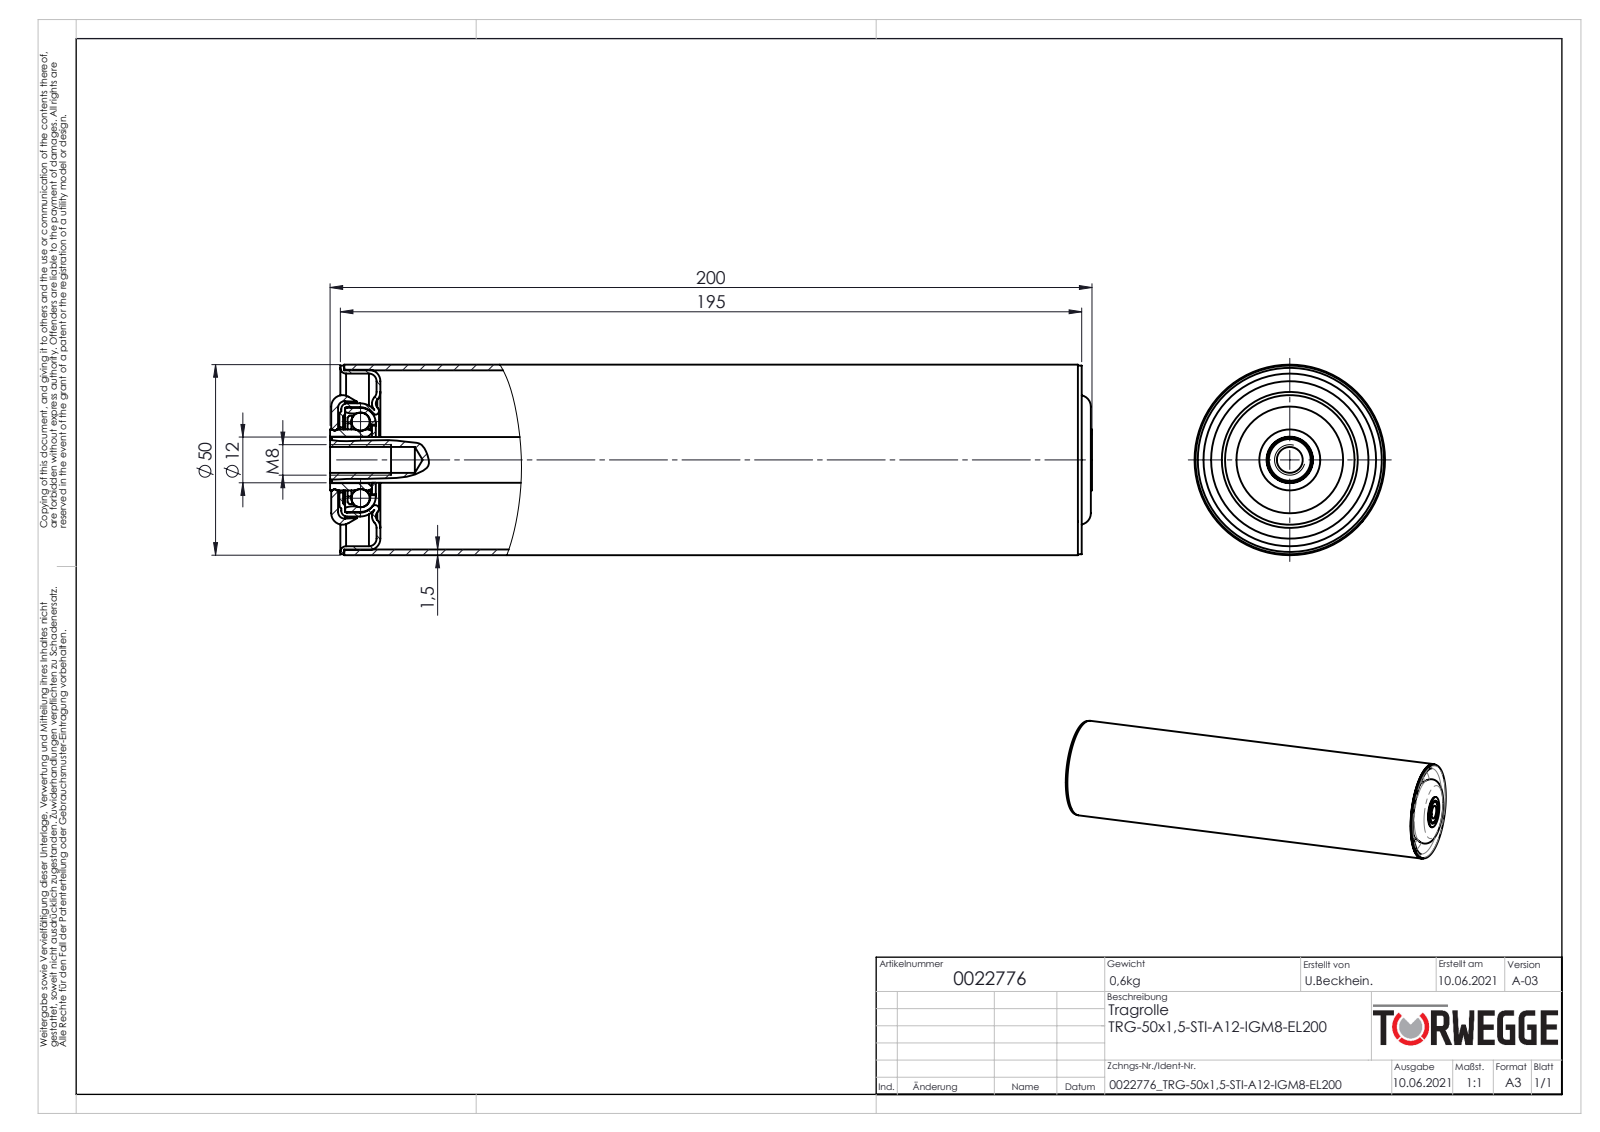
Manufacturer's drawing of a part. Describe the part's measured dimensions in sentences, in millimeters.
The part is named "0022776; 0026293_Typ-TRG-50x1,5-12; 0039771_Tragrollenrohr-Ø50x1,5STI_KFG_EL200; 0039780-Achse-ST-Ø12-KFG_IGM8-AL=200 (+1 more)". Its 3-D file was written by "SolidWorks 2020 (AUTOMOTIVE_DESIGN)". It is 30 solids with 498 faces: 92 planar, 102 cylindrical and 304 other. Overall it measures 200 by 50 by 50 millimeters. Its volume is 81 860 cubic millimeters and its surface area 97 629 square millimeters. Round holes: 1 of diameter 6.8, 1 of diameter 12, 1 of diameter 12.2, 1 of diameter 17.1, 1 of diameter 18.5, 1 of diameter 19.2, 1 of diameter 27.7, 1 of diameter 45.3, 1 of diameter 47. Round bosses or shafts: 1 of diameter 50, 1 of diameter 49.5, 1 of diameter 47.3, 1 of diameter 29.7, 1 of diameter 27.4, 1 of diameter 27.3, 1 of diameter 23.2, 1 of diameter 18. Partial cylindrical surfaces (rounded edges, fillets, slot ends): 1 of radius 8.85. The main face-to-face distances are 1, 1.8, 197.6, 9.75, 184.35, 11.9, 187.5, 10.1, 185.7, 12.9.
